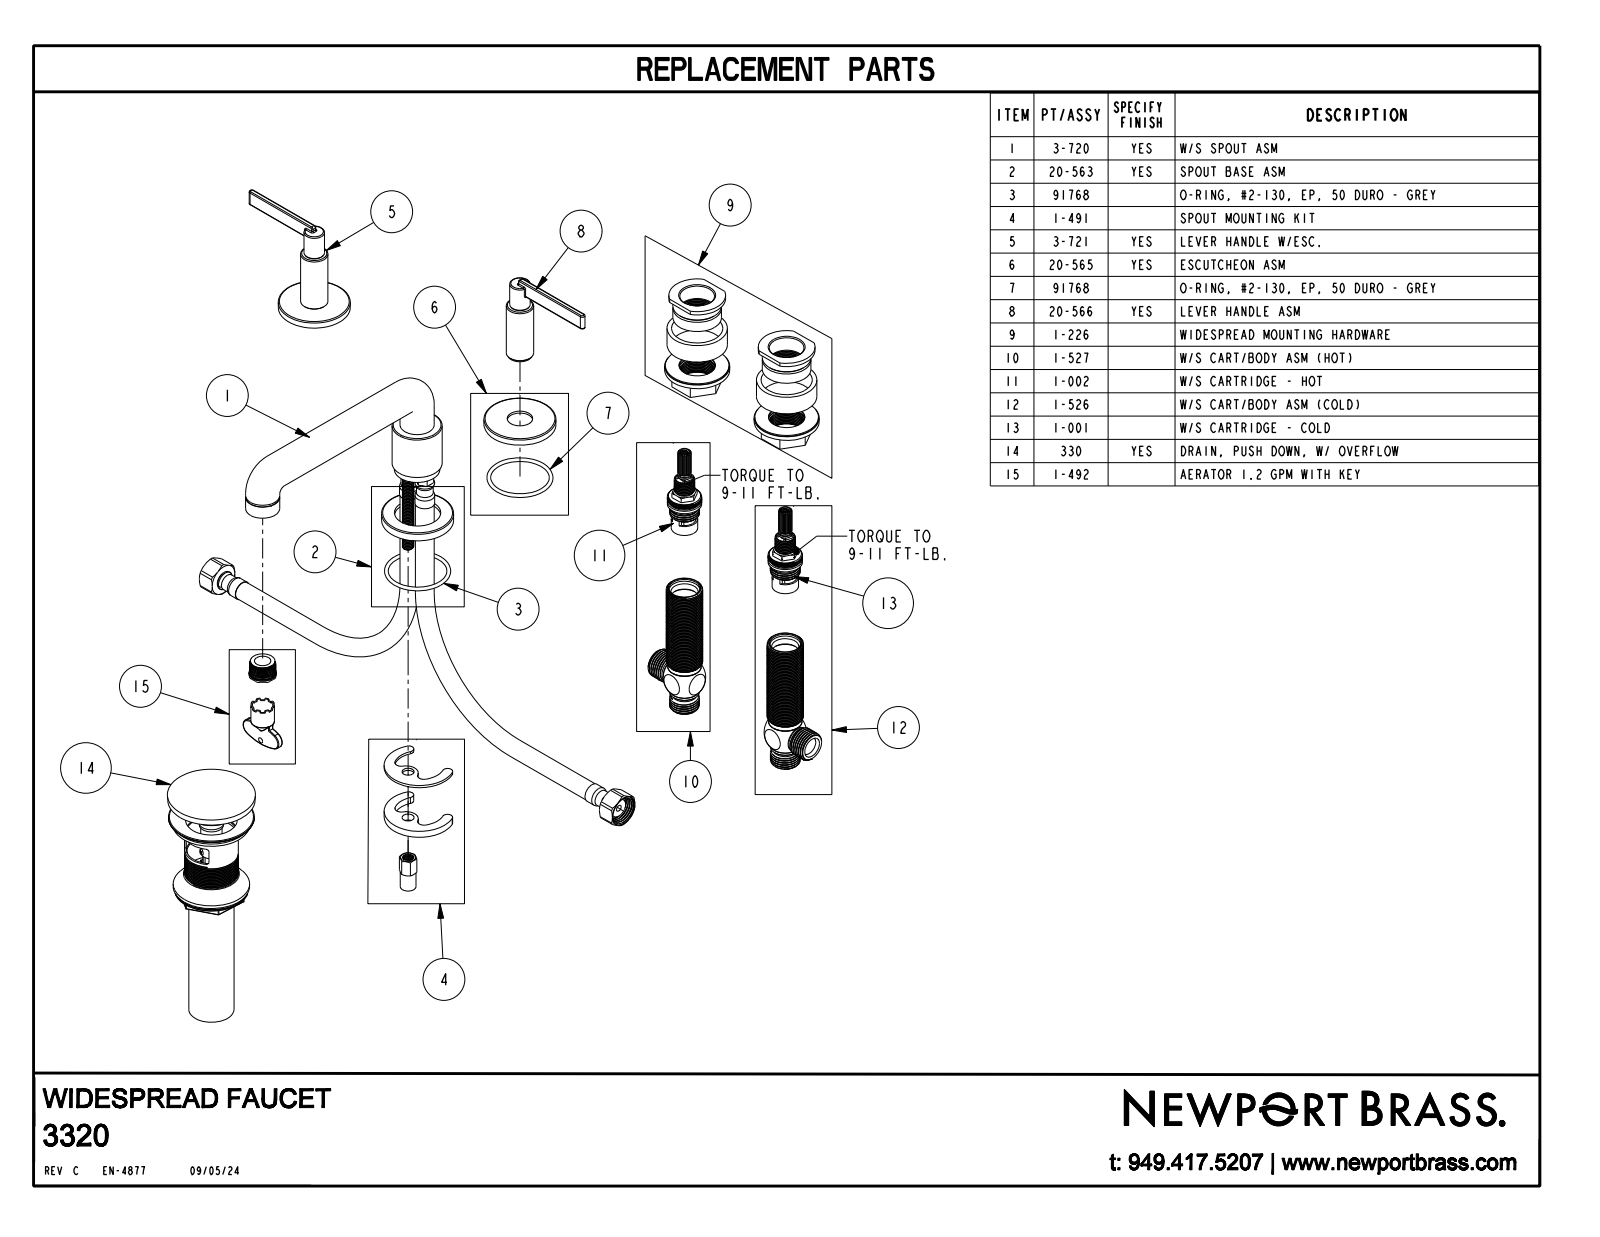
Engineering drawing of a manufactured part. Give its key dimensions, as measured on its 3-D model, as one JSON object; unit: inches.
{"part_name": "13530; 20-563_ASM; 13531; 30689 (+8 more)", "step_written_by": "CREO PARAMETRIC BY PTC INC, 2018400 (CONFIG_CONTROL_DESIGN)", "units": "inches", "bodies": {"solids": 10, "faces": 720, "planar": 190, "cylindrical": 345, "other": 185}, "overall_size": [13, 7.526, 3.211], "volume_in3": 6.678, "surface_area_in2": 109.7, "round_holes": [[0.679, 3], [1.6, 3], [0.11, 2], [0.25, 2], [0.354, 2], [0.36, 2], [0.397, 2], [0.4, 2], [0.423, 2], [0.516, 2], [0.535, 2], [0.6, 2]], "round_bosses_or_shafts": [[0.939, 3], [0.75, 3], [2, 2], [1.65, 2], [0.73, 2], [0.68, 2], [0.563, 2], [0.51, 2]], "partial_cylinders_radius": [[0.03, 16], [0.06, 2], [0.075, 2], [0.137, 2]], "face_to_face_distances": [0.05, 0.1, 0.15, 0.2, 0.07, 0.12, 0.17, 0.25, 0.08, 0.15], "hole_center_spacings": [0.3, 0.461, 3.7, 4, 4.015, 4.3, 6.015, 7.217]}
